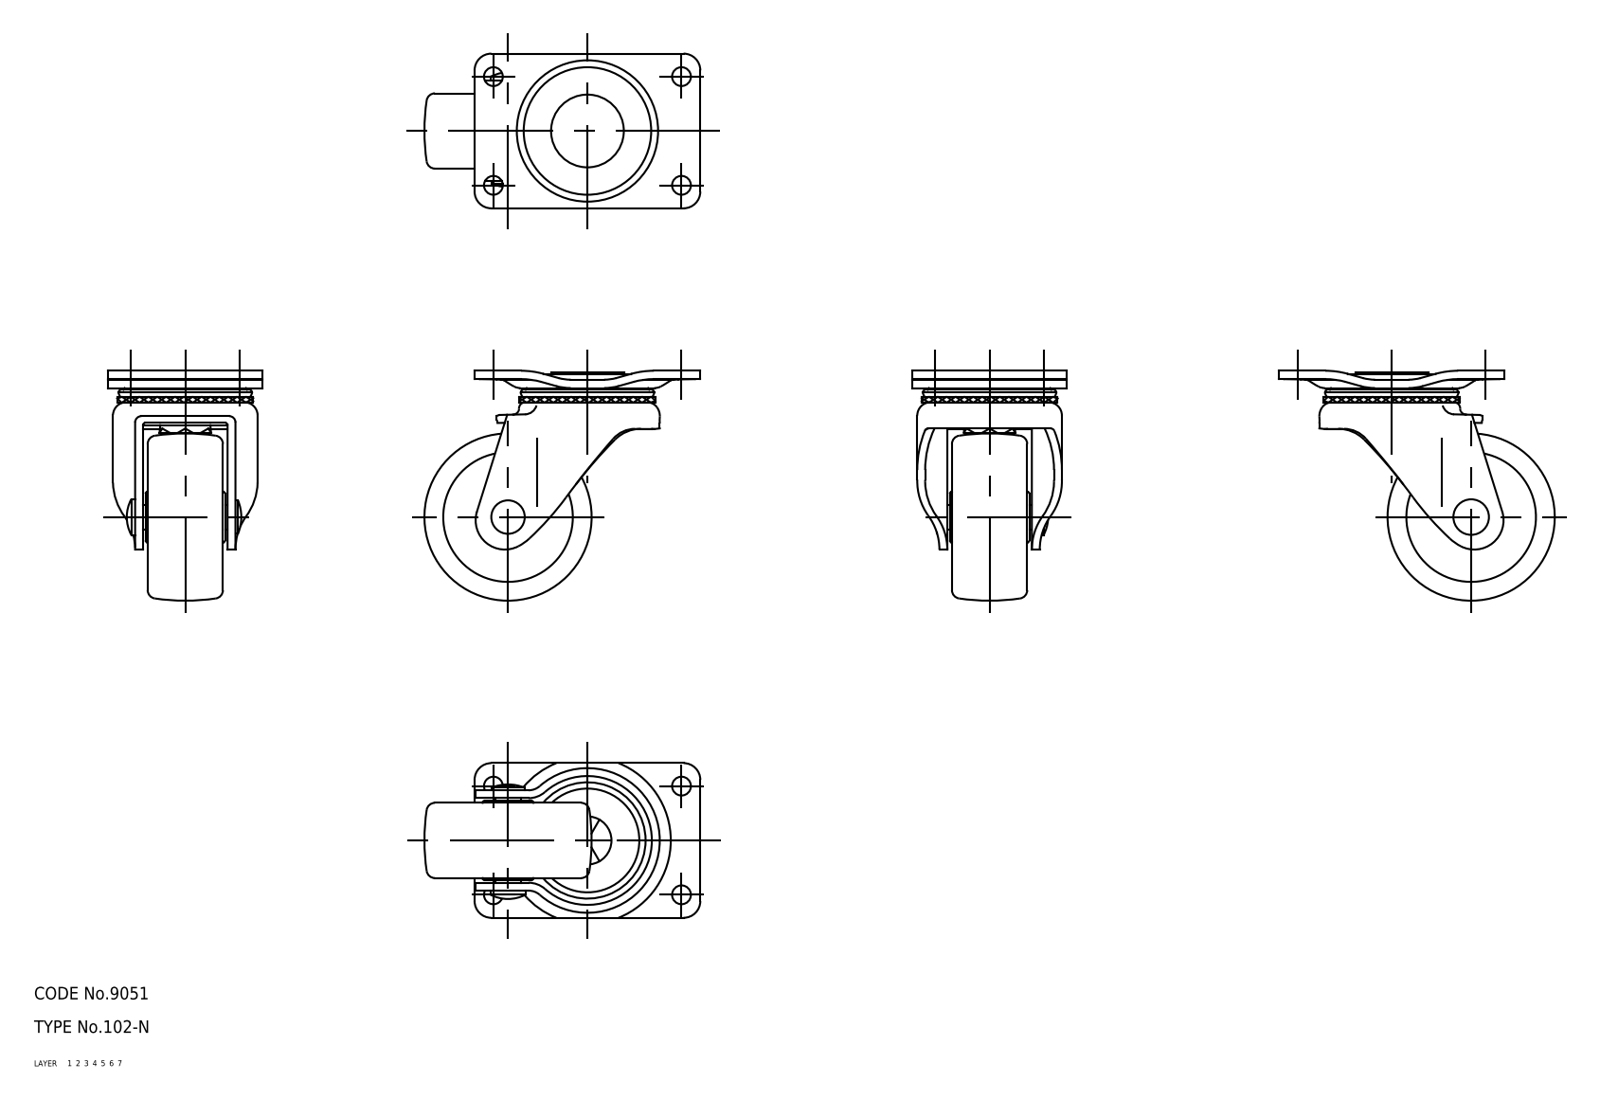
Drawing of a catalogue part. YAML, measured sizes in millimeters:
part_name: "wheel; mounting plate; main shaft; axle (+1 more)"
step_written_by: "CADfix (AUTOMOTIVE_DESIGN)"
units: millimeters
bodies: {solids: 5, faces: 271, planar: 0, cylindrical: 0, other: 271}
overall_size: [66, 55, 37]
volume: 29318
surface_area: 18851
